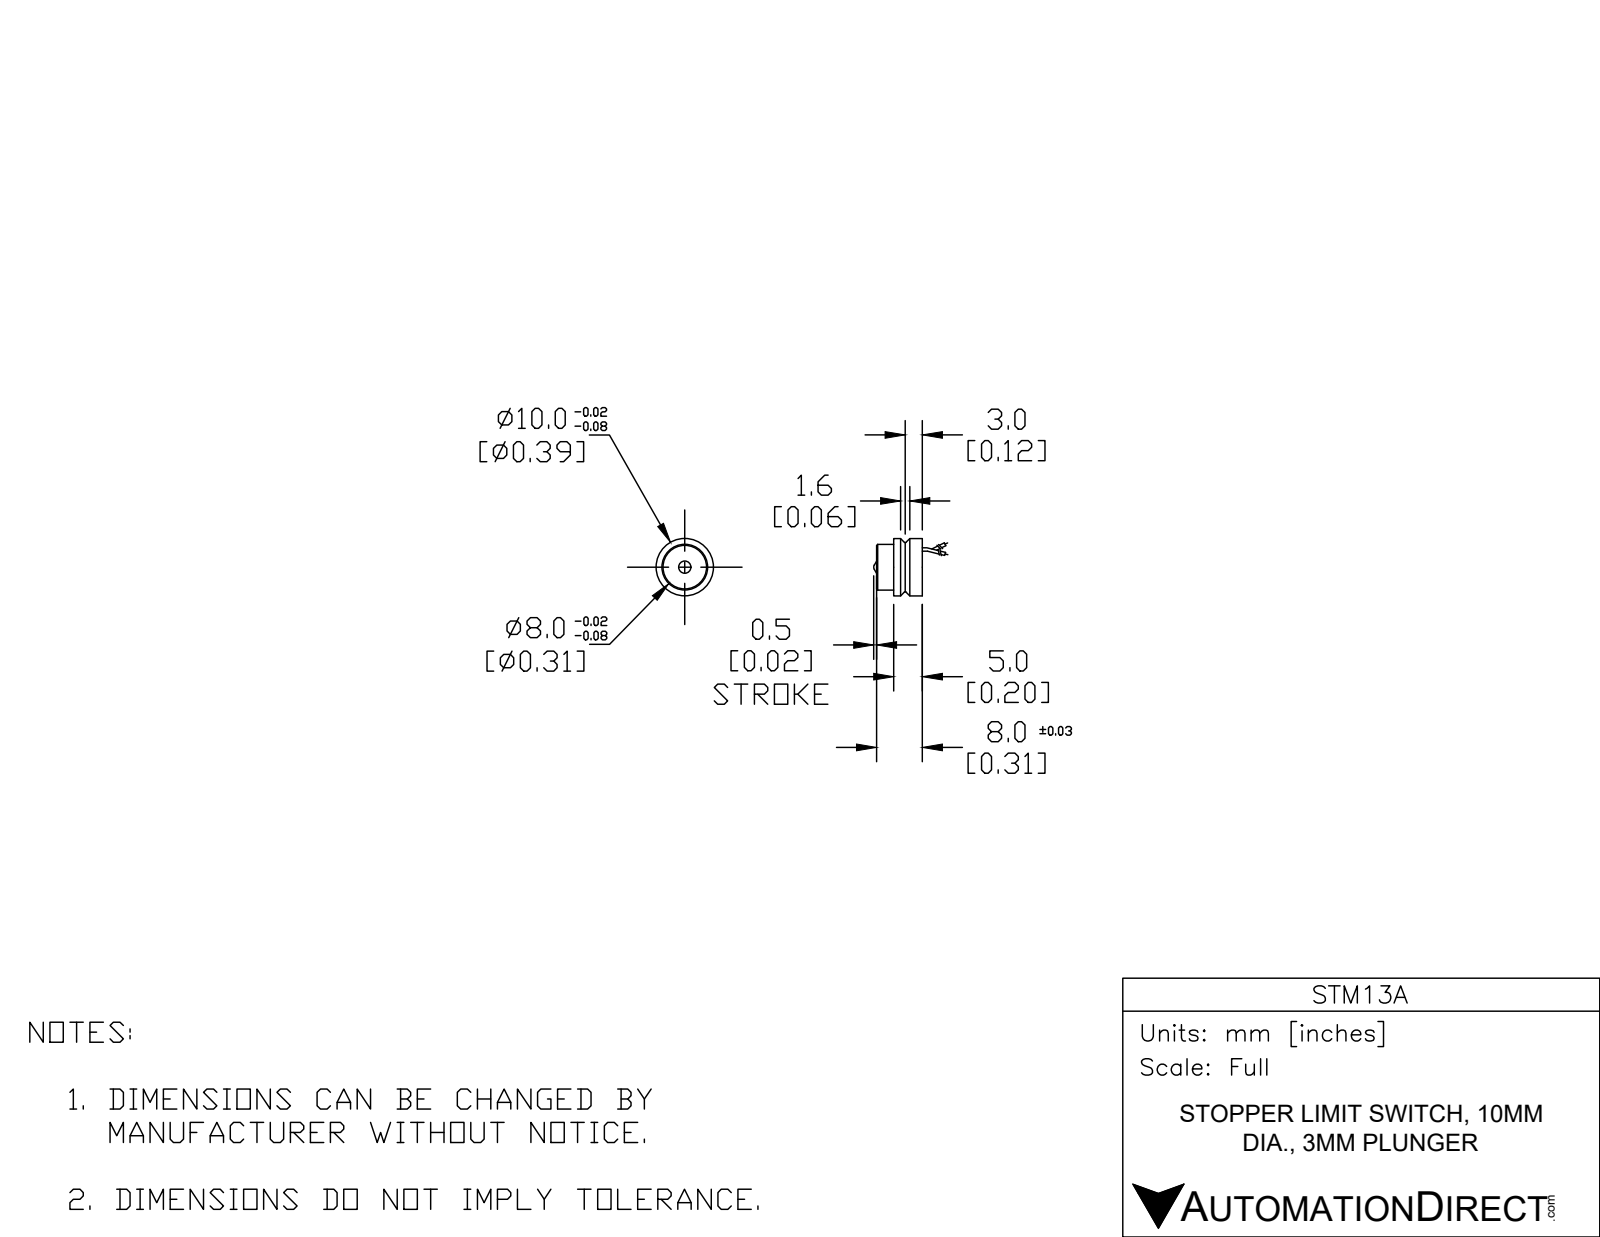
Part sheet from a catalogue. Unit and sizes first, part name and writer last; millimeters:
Units: millimetres
Overall size (bounding box): 18.5 × 10 × 10
Round bosses / shafts (diameter × count): ⌀0.6 ×2, ⌀10 ×1, ⌀8 ×1
Main face-to-face distances: 8, 3, 5, 18, 15, 10
Volume: 531 mm³ · Surface area: 438 mm²
Bodies: 1 solid, 29 faces (5 planar, 10 cylindrical, 14 other)
STEP written by: Spatial InterOp 3D (CONFIG_CONTROL_DESIGN)
